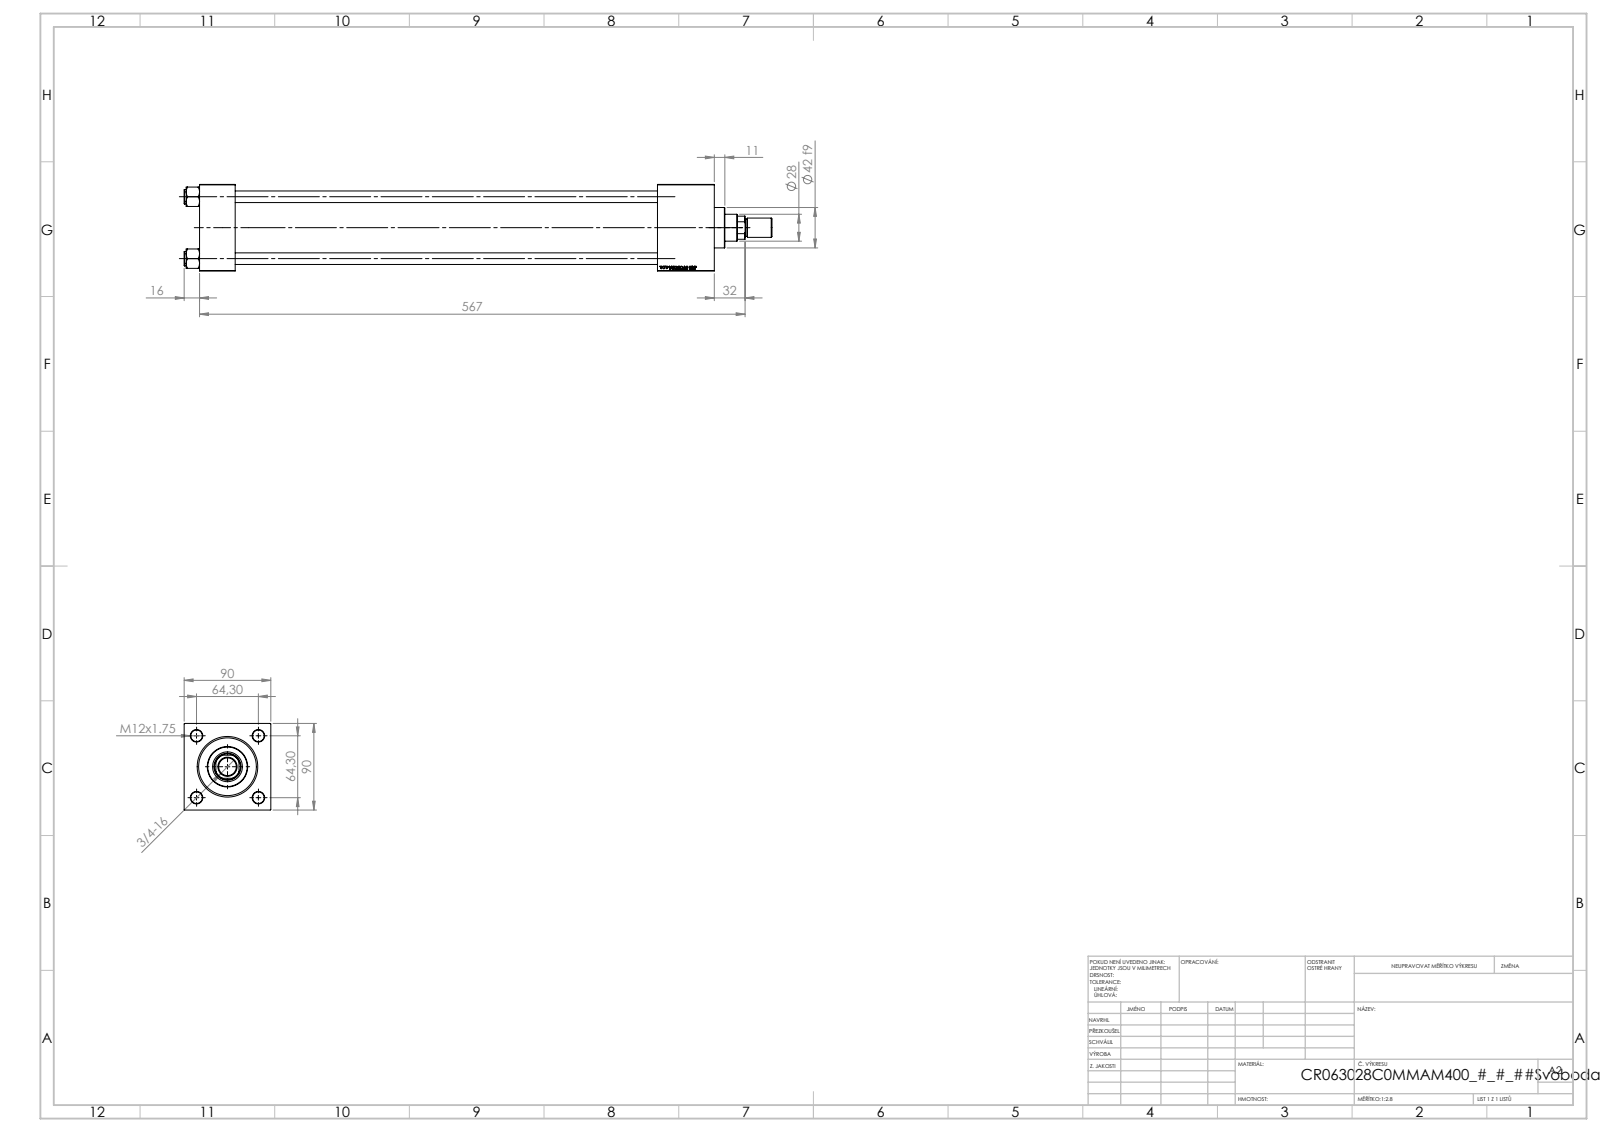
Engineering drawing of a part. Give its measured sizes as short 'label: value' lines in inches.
name: NUT_M5_C; V215CR_VCP_C; ROD_END_AH; V215_VC_A (+2 more)
written by: SolidWorks 2019 (CONFIG_CONTROL_DESIGN)
unit: in
bodies: 12 solids, 1162 faces (530 planar, 90 cylindrical, 542 other)
size: 24.055 × 3.543 × 3.543
volume: 97.52 in³; area: 666.1 in²
holes: 4× ⌀0.472, 2× ⌀0.276, 2× ⌀0.825, 2× ⌀1.181, 1× ⌀0.728, 1× ⌀1.102, 1× ⌀1.22, 1× ⌀1.969, 1× ⌀2.362, 1× ⌀2.48
bosses: 4× ⌀0.591, 1× ⌀2.717, 1× ⌀1.654, 1× ⌀0.787, 1× ⌀0.709
rounds: 1× R0.531
face distances: 3.543, 1.457, 21.063, 19.606, 18.74, 17.283, 2.323, 19.933, 18.476, 1.193
hole spacings: 1.79, 2.531, 3.58, 18.799
